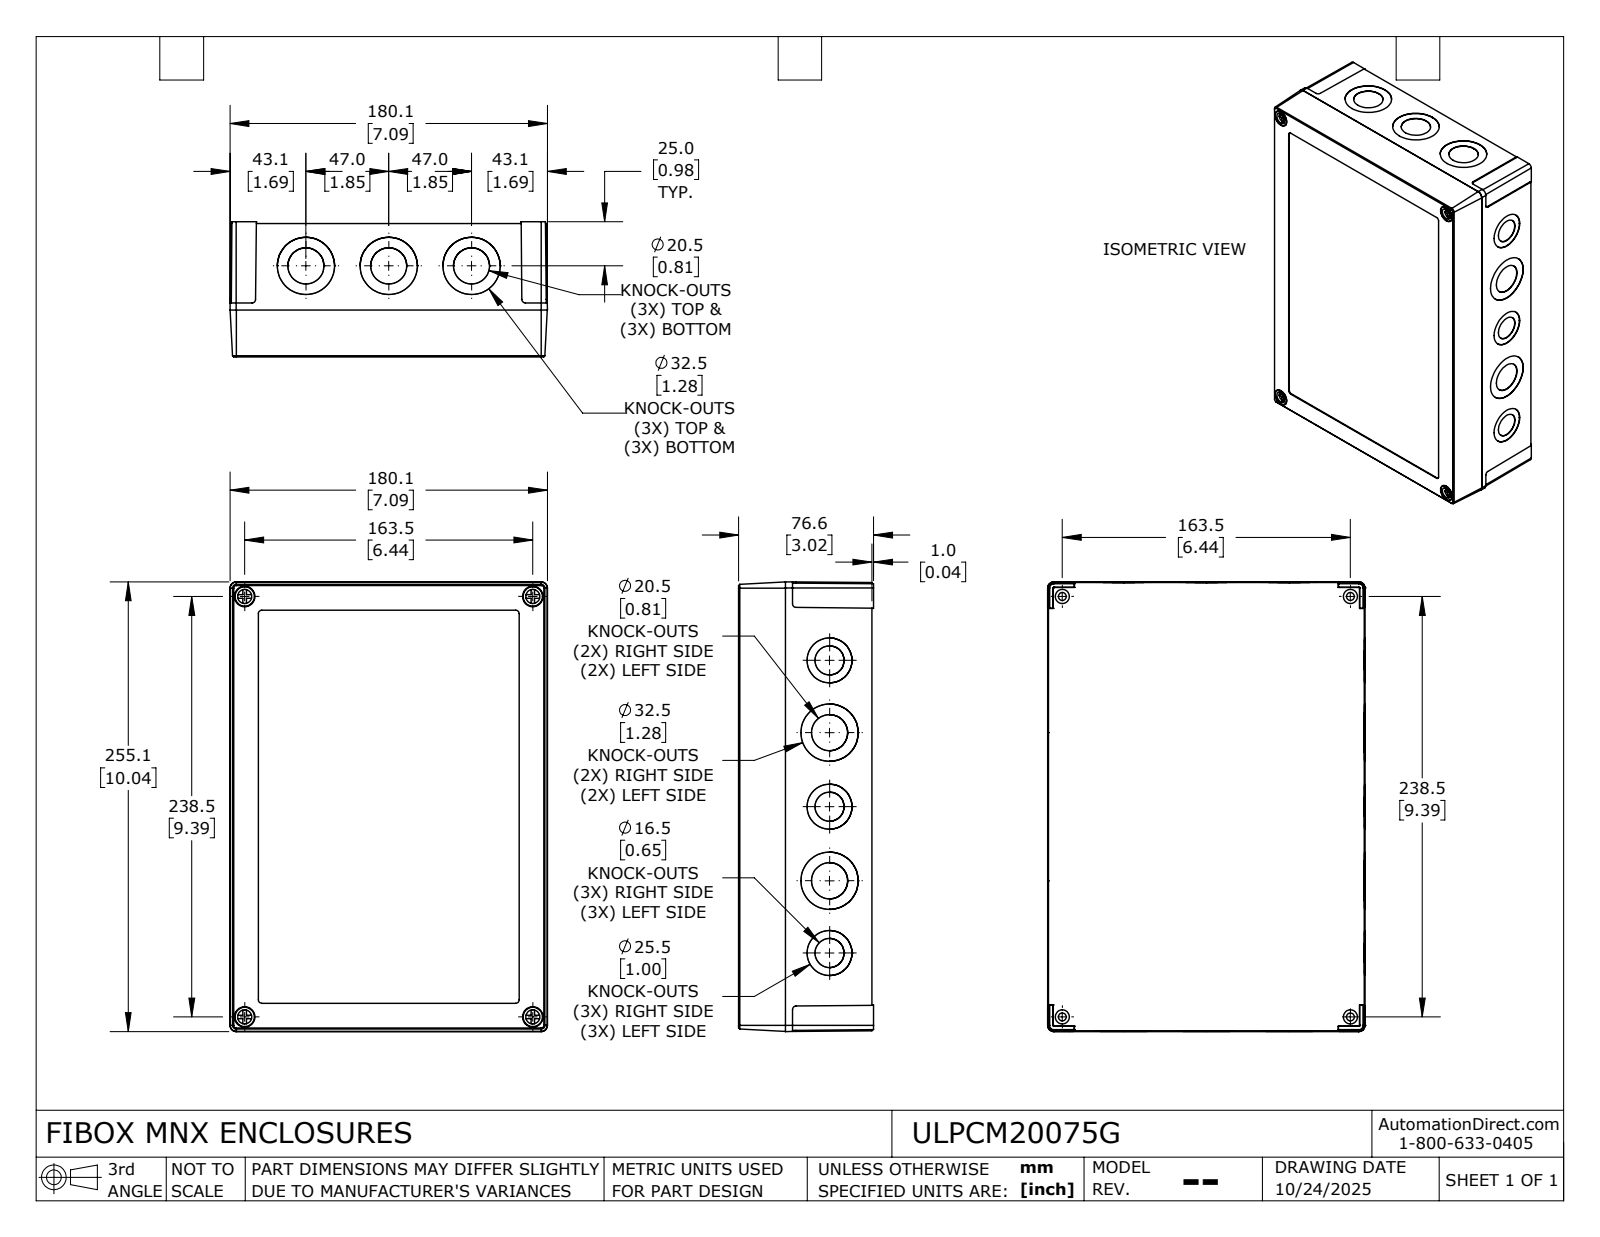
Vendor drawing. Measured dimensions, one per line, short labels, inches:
name: ULPCM20075G_Default
written by: SolidWorks 2024 (CONFIG_CONTROL_DESIGN)
unit: in
bodies: 6 solids, 678 faces (350 planar, 272 cylindrical, 56 other)
size: 10.043 × 7.091 × 3.016
volume: 30.24 in³; area: 502 in²
holes: 20× ⌀0.126, 20× ⌀0.157, 10× ⌀0.807, 10× ⌀1.28, 6× ⌀0.65, 6× ⌀1.004, 4× ⌀0.177, 4× ⌀0.315, 4× ⌀0.457
bosses: 16× ⌀0.315, 4× ⌀0.433, 4× ⌀0.283, 4× ⌀0.276
rounds: 8× R0.079, 6× R0.112, 4× R0.042, 4× R0.197, 2× R0.046
face distances: 2.87, 0.118, 2.752, 0.087, 2.957, 2.839, 0.165, 2.858, 0.02, 0.106
hole spacings: 4.921, 1.939, 5.046, 0.812, 0.872, 1.046, 1.333, 1.508
